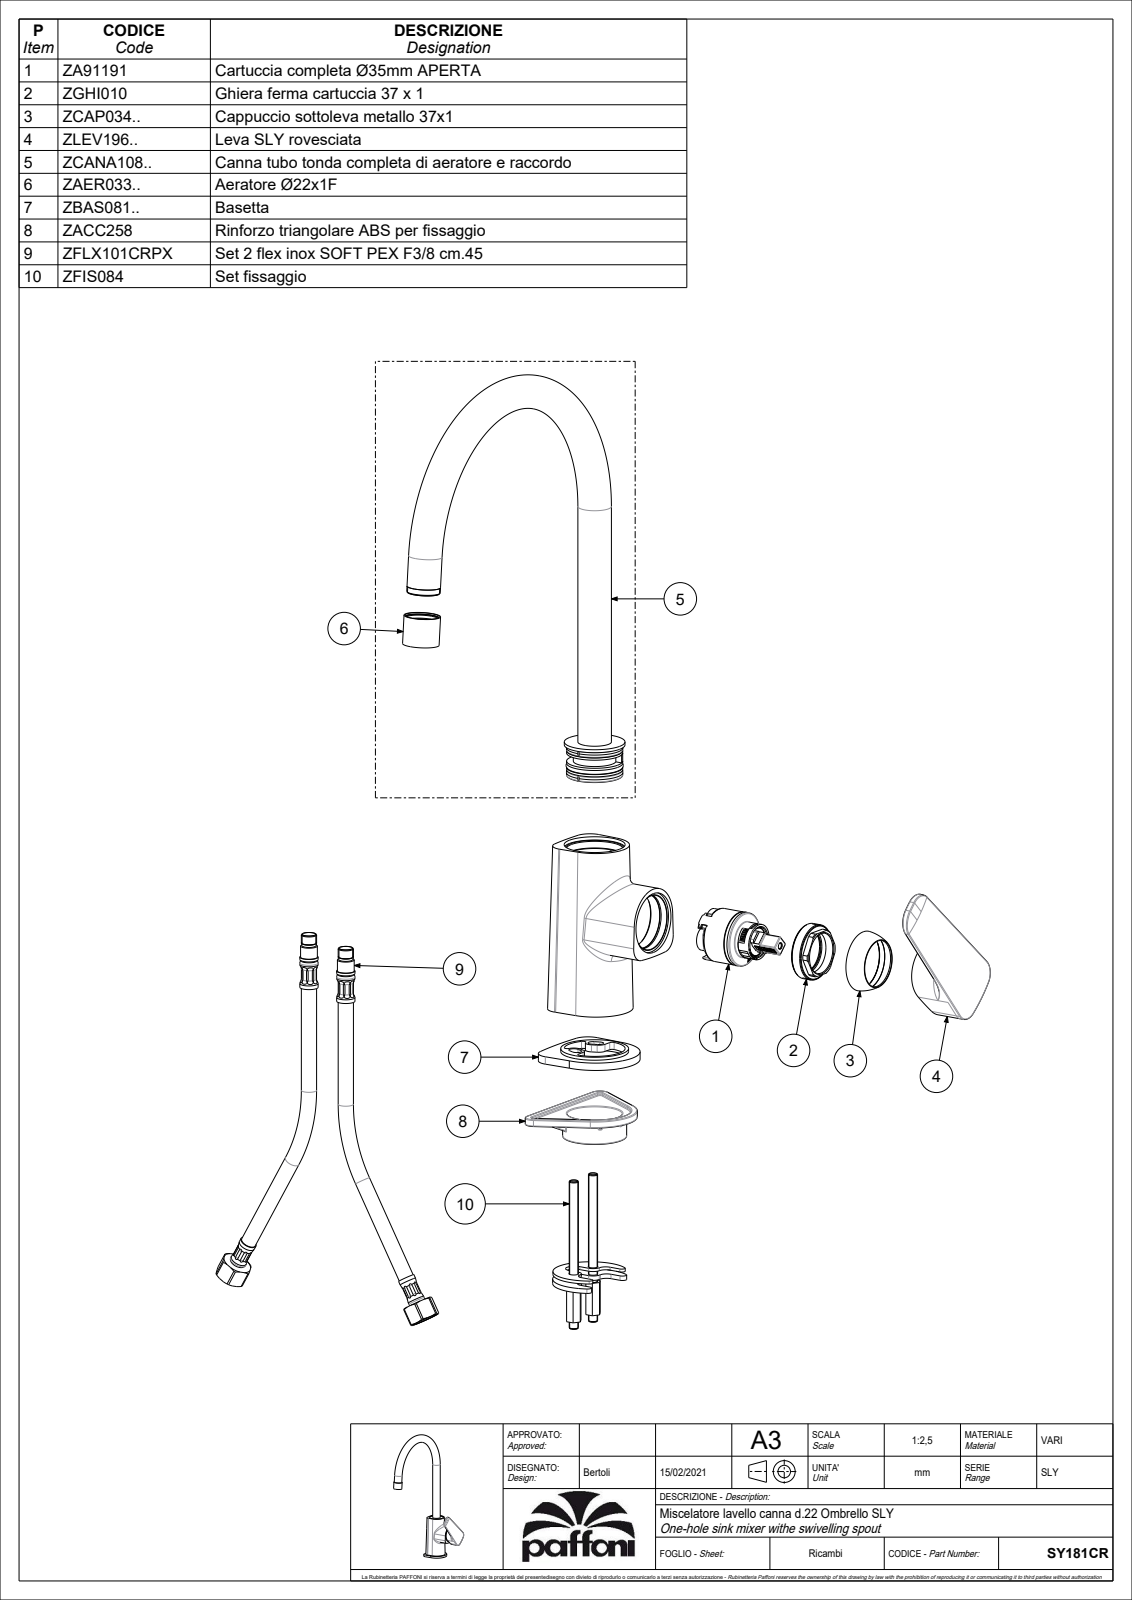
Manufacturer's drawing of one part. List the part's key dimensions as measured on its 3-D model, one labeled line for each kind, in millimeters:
Part name (STEP PRODUCT): SY181CR
STEP written by: CREO PARAMETRIC BY PTC INC, 2020044 (CONFIG_CONTROL_DESIGN)
Units: millimetres
Bodies: 3 solids, 3323 faces (2401 planar, 515 cylindrical, 407 other)
Overall size (bounding box): 383.3 × 238.61 × 108.95
Volume: 273 537 mm³ · Surface area: 154 811 mm²
Round holes (diameter × count): ⌀7 ×4, ⌀5.5 ×3, ⌀5 ×2, ⌀8 ×2, ⌀9 ×2, ⌀11 ×2, ⌀19.6 ×2, ⌀38 ×2, ⌀40 ×2, ⌀3 ×1, ⌀3.3 ×1, ⌀3.4 ×1
Round bosses / shafts (diameter × count): ⌀22 ×2, ⌀4.8 ×2, ⌀4 ×2, ⌀44.5 ×1, ⌀39.8 ×1, ⌀36.8 ×1, ⌀35.4 ×1, ⌀35 ×1
Partial cylindrical surfaces — rounded edges, fillets, slot ends (radius × count): R0.5 ×44, R1.5 ×13, R1 ×10, R3 ×10, R1.7 ×6, R2 ×5, R0.2 ×4, R0.8 ×4
Main face-to-face distances: 2, 5, 7, 1.5, 2.2, 33, 5.5, 7.5, 2.8, 6
Hole centre spacings: 8.5, 8.61, 9.6, 13.46, 14.21, 15.14, 15.4, 21.94
